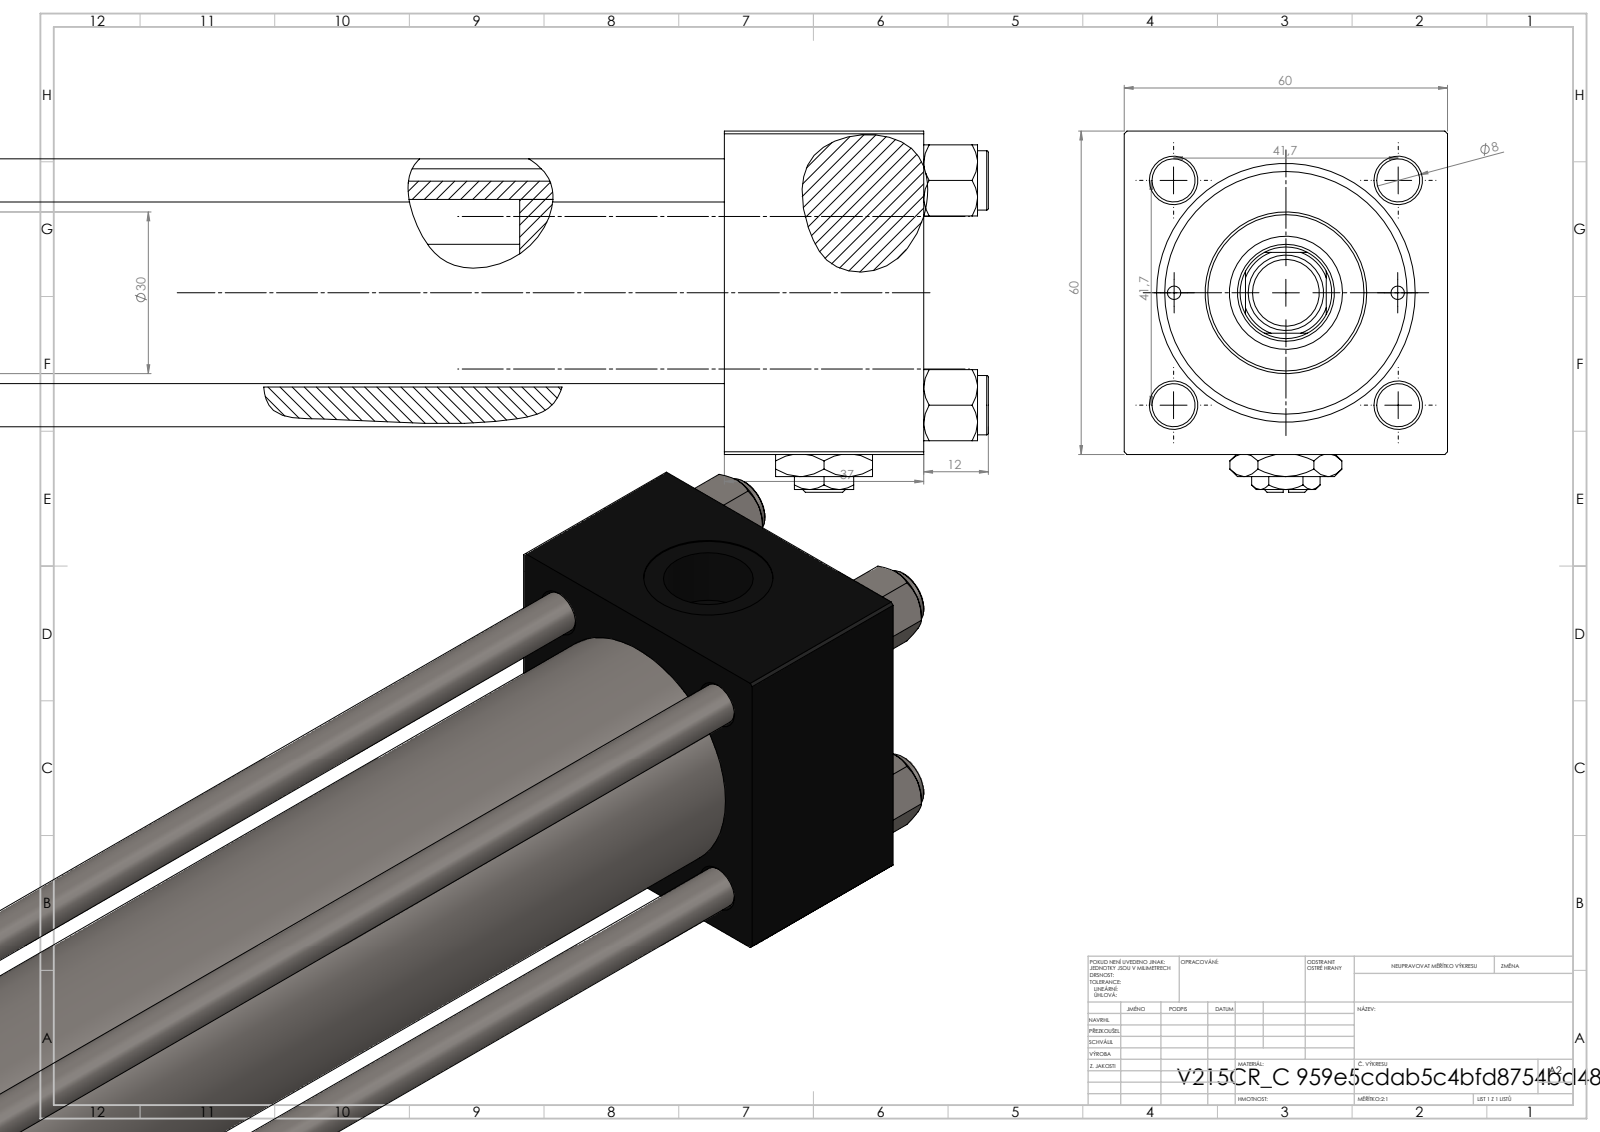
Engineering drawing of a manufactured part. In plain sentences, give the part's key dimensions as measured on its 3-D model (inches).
The part is named "ROD_END_AH; NUT_M5_C; V215CR_VCP_C; V215CR_C_Body (+3 more)". Its 3-D file was written by "SolidWorks 2019 (CONFIG_CONTROL_DESIGN)". It is 14 solids with 1270 faces: 580 planar, 106 cylindrical and 584 other. Overall it measures 13.504 by 2.638 by 2.362 inches. Its volume is 31.85 cubic inches and its surface area 262.5 square inches. Round holes: 4 of diameter 0.315, 2 of diameter 0.098, 2 of diameter 0.276, 2 of diameter 0.656, 2 of diameter 0.945, 1 of diameter 0.335, 1 of diameter 0.709, 1 of diameter 0.827, 1 of diameter 1.22, 1 of diameter 1.575, 1 of diameter 1.772. Round bosses or shafts: 4 of diameter 0.433, 1 of diameter 1.811, 1 of diameter 1.181, 1 of diameter 0.551, 1 of diameter 0.472. Partial cylindrical surfaces (rounded edges, fillets, slot ends): 1 of radius 0.335. The main face-to-face distances are 2.362, 1.457, 11.339, 9.882, 2.087, 9.252, 7.795, 10.209, 8.752, 0.957. The hole center spacings are 0.821, 1.161, 1.642, 1.832, 0.817, 2.322, 1.634, 9.154.
